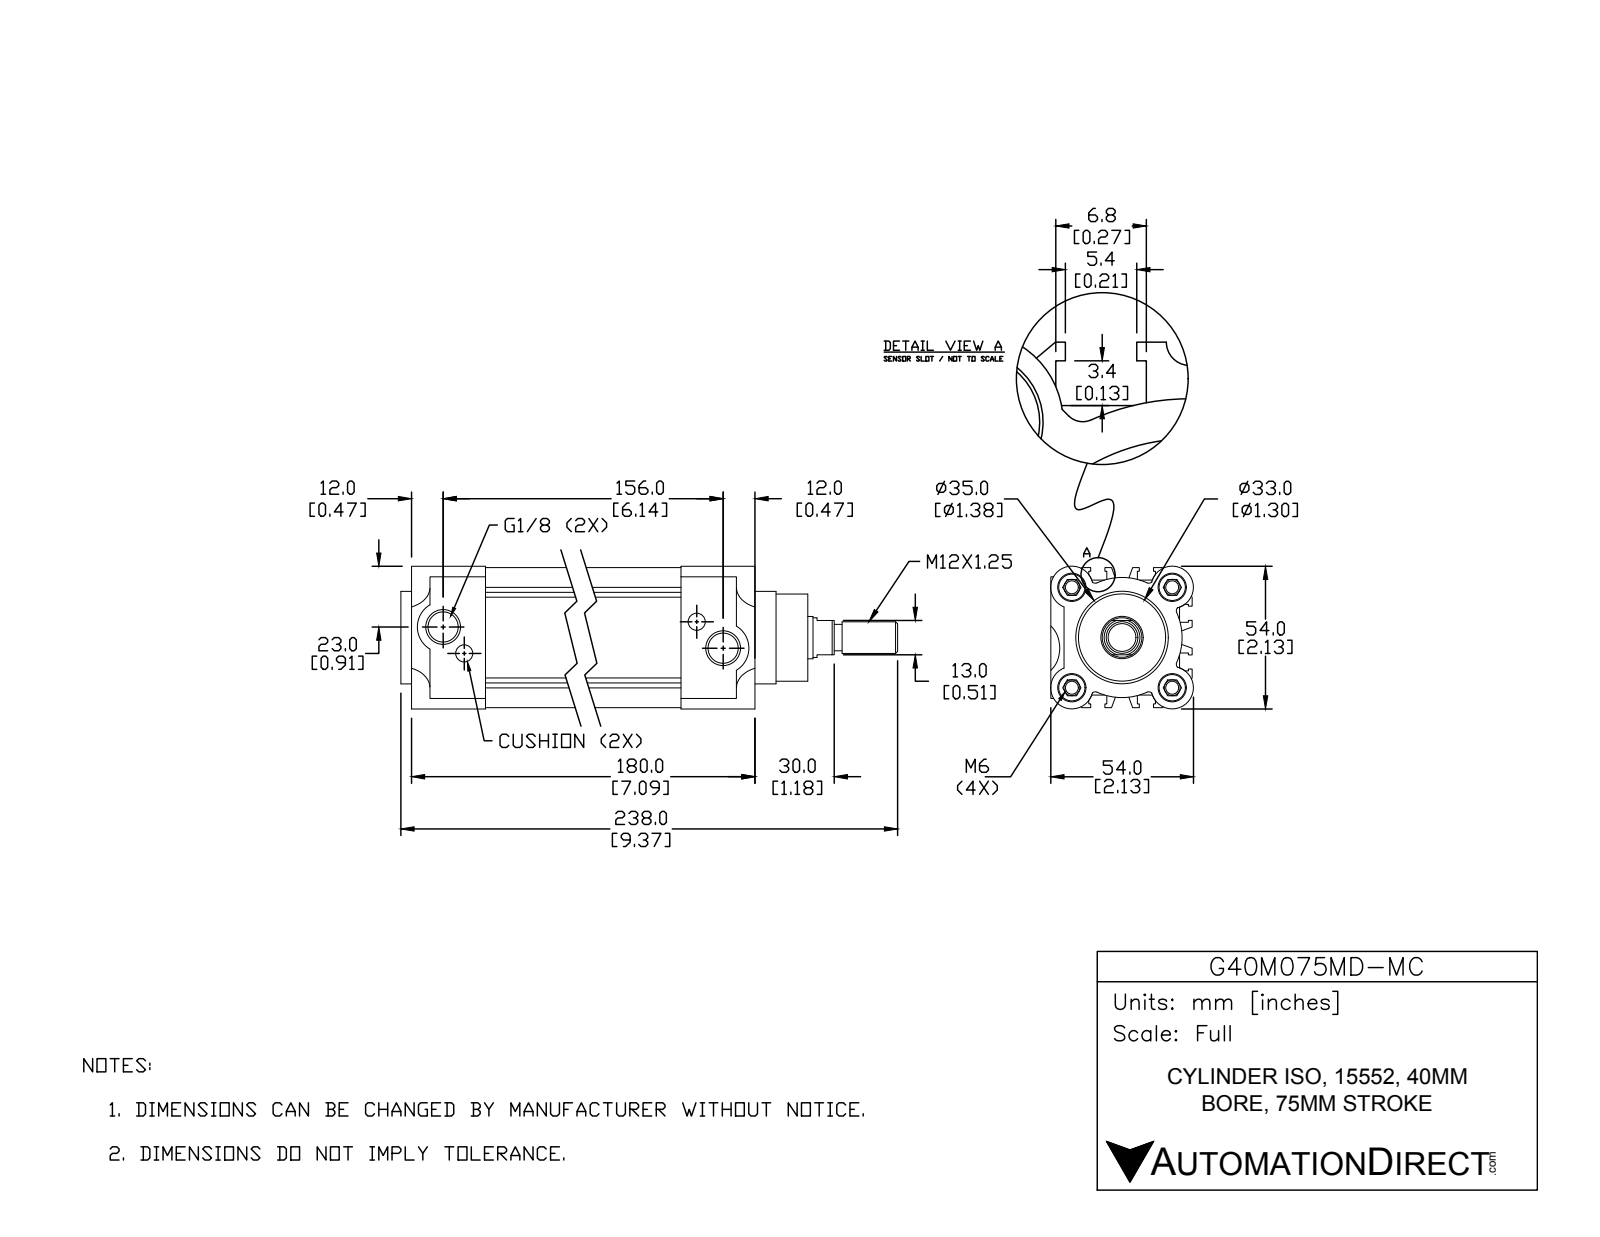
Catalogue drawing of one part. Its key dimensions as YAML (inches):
part_name: "G40M075MD-MC; 4012175-R; 40-HL; 40121-HR (+1 more)"
step_written_by: "SolidWorks 2015 (CONFIG_CONTROL_DESIGN)"
units: inches
bodies: {solids: 4, faces: 418, planar: 236, cylindrical: 138, other: 44}
overall_size: [9.37, 2.126, 2.126]
volume: 23.32
surface_area: 174.2
round_holes:
  - {diameter: 0.194, count: 4}
  - {diameter: 0.421, count: 4}
  - {diameter: 0.256, count: 2}
  - {diameter: 0.451, count: 2}
  - {diameter: 0.63, count: 1}
round_bosses_or_shafts:
  - {diameter: 0.394, count: 5}
  - {diameter: 1.575, count: 1}
  - {diameter: 1.378, count: 1}
  - {diameter: 1.299, count: 1}
  - {diameter: 0.591, count: 1}
  - {diameter: 0.472, count: 1}
partial_cylinders:
  - {radius: 0.059, count: 12}
  - {radius: 0.004, count: 6}
  - {radius: 0.295, count: 4}
  - {radius: 0.315, count: 4}
  - {radius: 0.384, count: 2}
  - {radius: 0.886, count: 1}
  - {radius: 0.896, count: 1}
face_to_face_distances: [1.9, 0.187, 4.606, 0.276, 1.378, 2.087, 0.724, 0.954, 1.372, 0.547]
hole_center_spacings: [1.058, 1.496, 2.116, 0.504, 0.557, 5.454, 5.748, 5.827]
